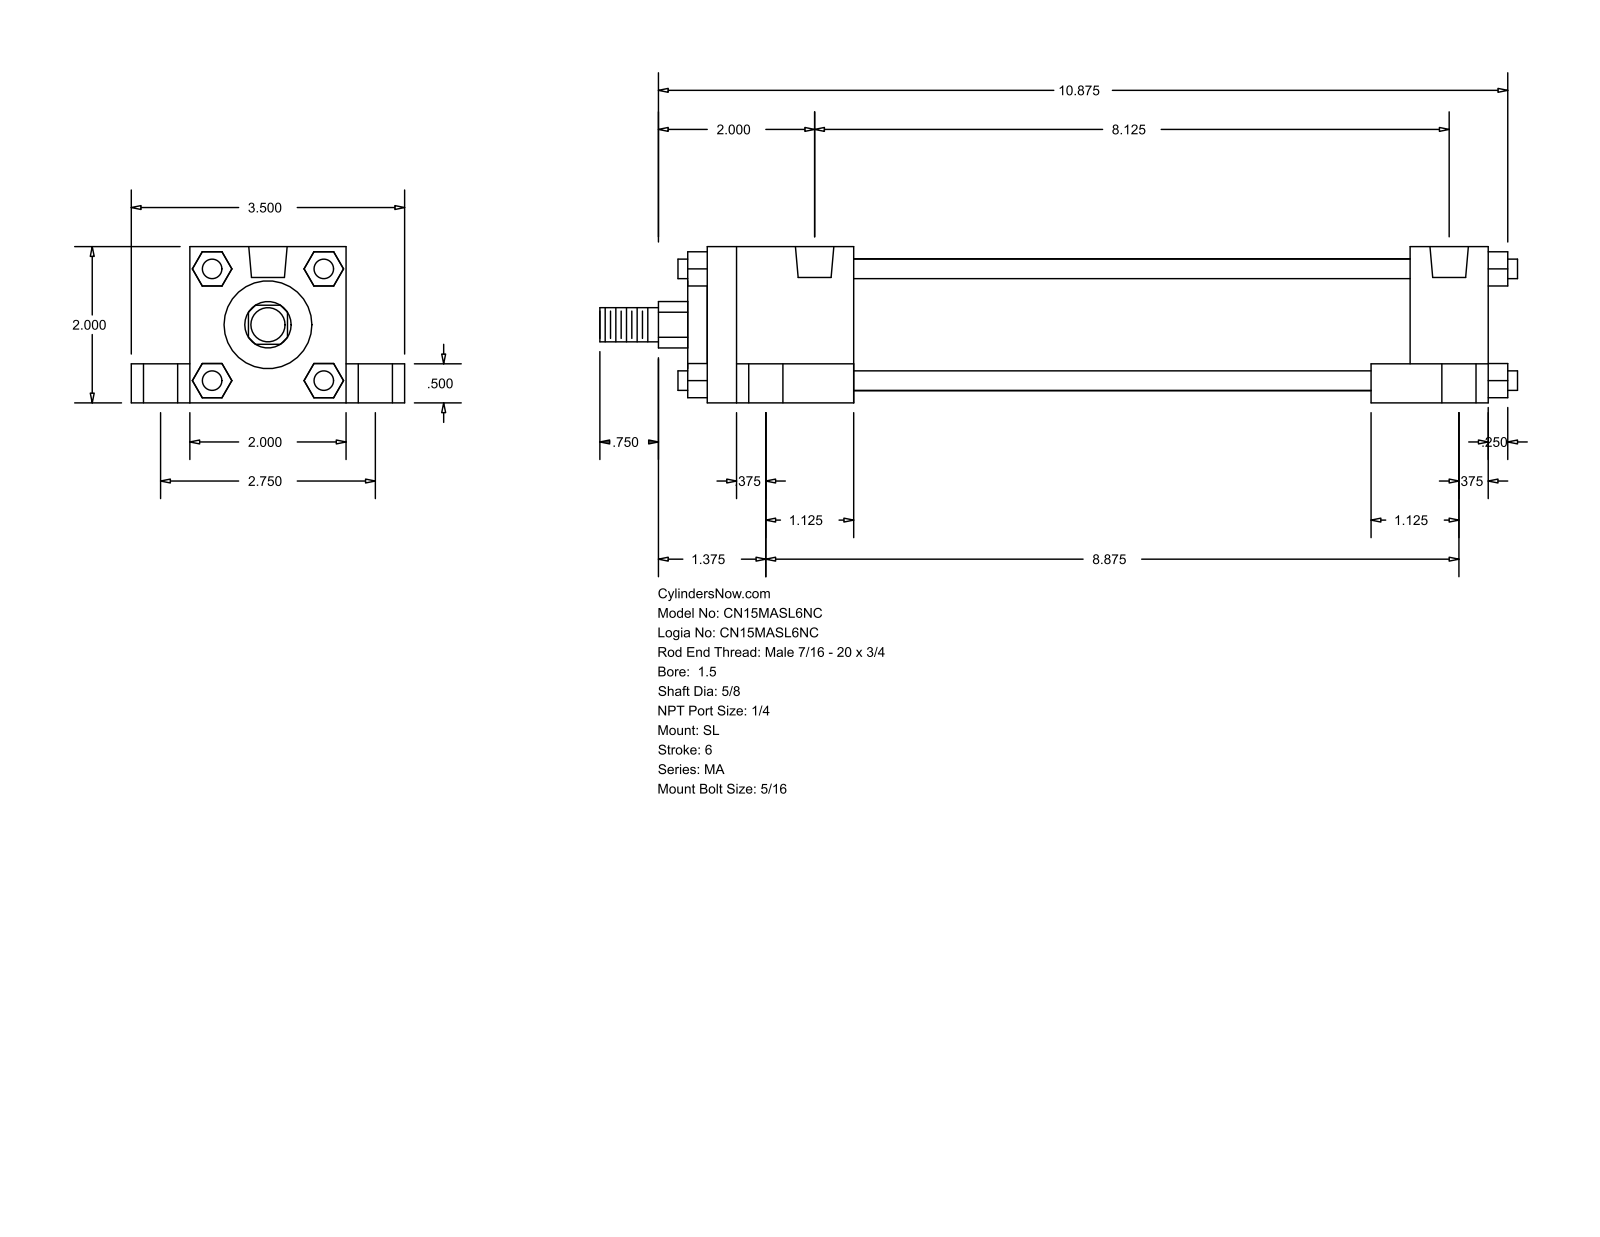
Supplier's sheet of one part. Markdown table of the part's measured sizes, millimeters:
| quantity | value |
| --- | --- |
| part name | MA_SL__0150_0.625 |
| STEP written by | GSSL Pune (CONFIG_CONTROL_DESIGN) |
| units | millimeters |
| bodies | 0 solids, 148 faces (112 planar, 36 cylindrical, 0 other) |
| overall size | 298.45 × 88.9 × 50.8 |
| round holes (diameter × count) | 7.94 × 4, 11.11 × 4, 17.46 × 4, 12.49 × 2 |
| round bosses / shafts (diameter × count) | 6.35 × 4, 42.93 × 1, 28.57 × 1, 15.88 × 1, 11.11 × 1 |
| partial cylindrical surfaces (radius × count) | 7.54 × 1 |
| main face-to-face distances | 50.8, 19.05, 38.1, 254, 69.85, 12.7, 180.97, 9.52, 6.35, 260.35 |
| hole center spacings | 35.06, 38.36, 69.84, 206.38, 212.44, 224.99, 225.43, 236 |
